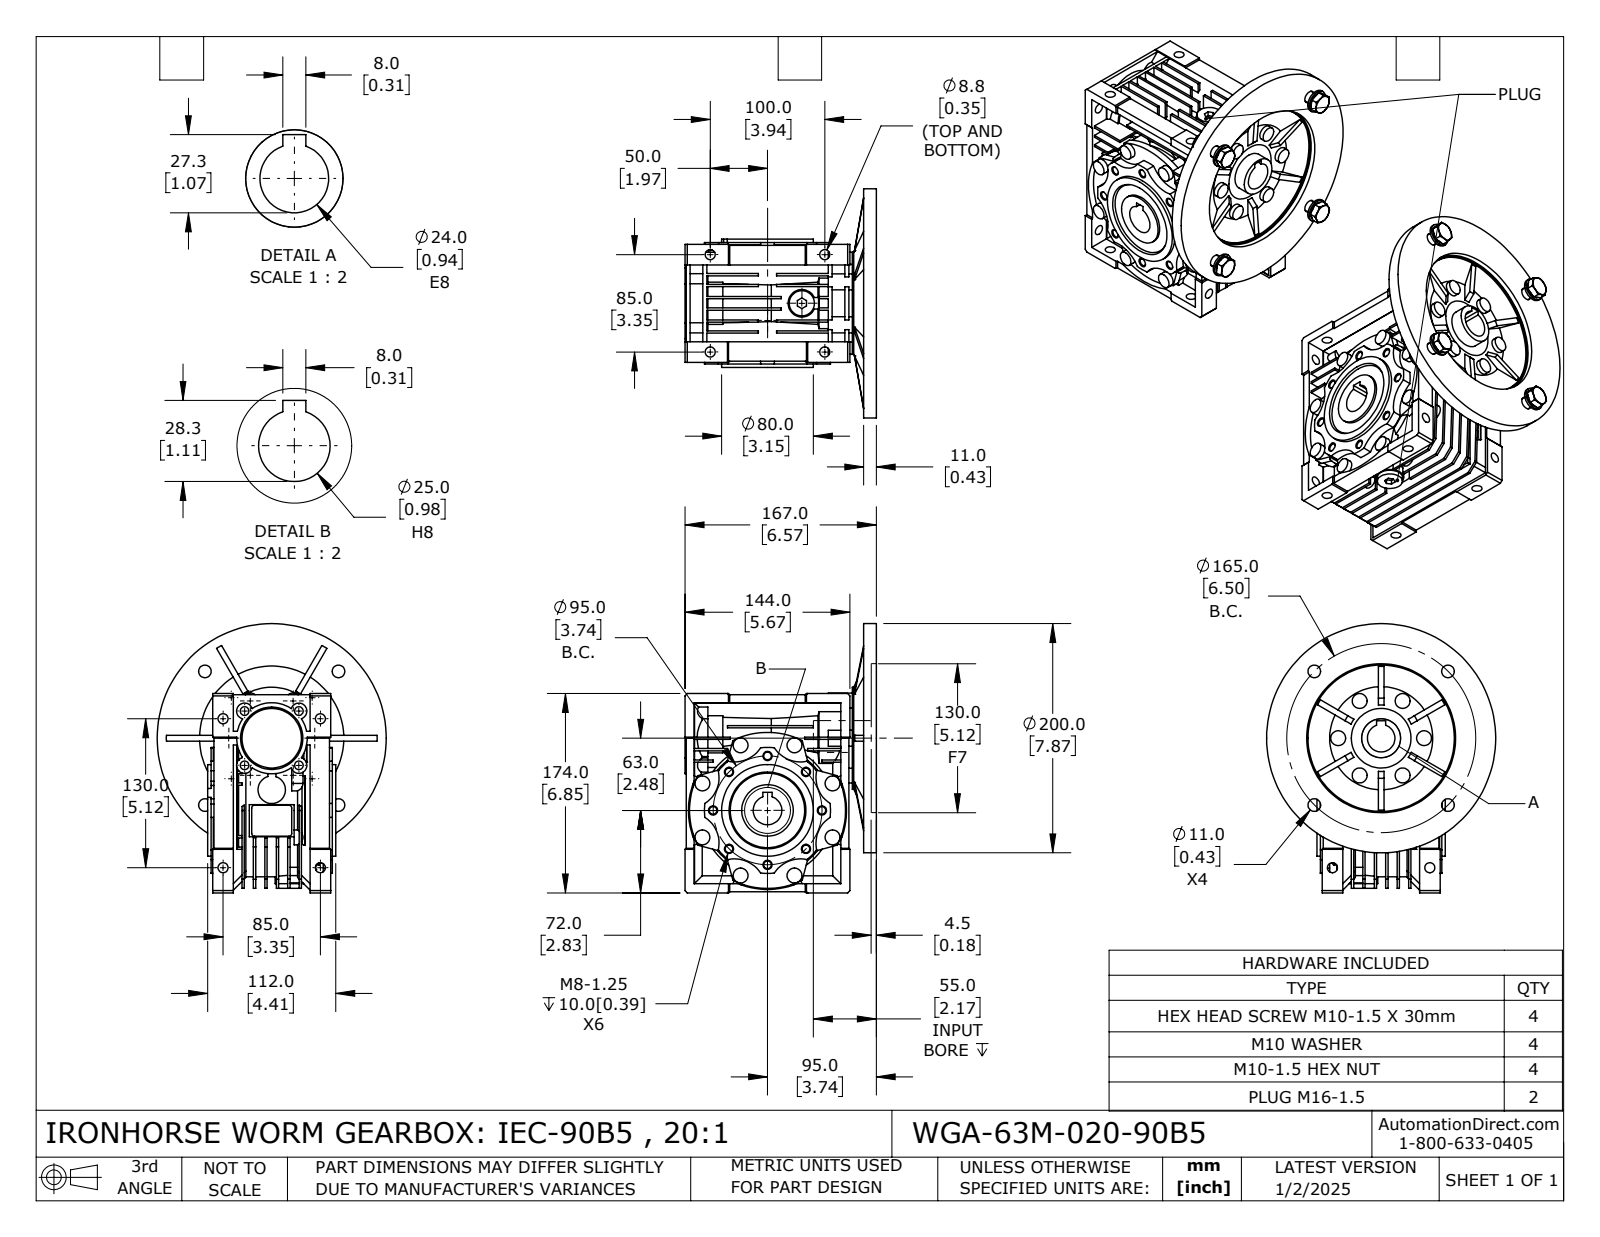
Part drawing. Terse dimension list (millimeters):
name: WGA-63M-020-90B5
written by: SolidWorks 2024 (CONFIG_CONTROL_DESIGN)
unit: mm
bodies: 20 solids, 1529 faces (897 planar, 394 cylindrical, 238 other)
size: 235 × 200 × 183.43
volume: 2 020 000 mm³; area: 402 901 mm²
holes: 8× ⌀6.65, 8× ⌀8.78, 4× ⌀7.56, 4× ⌀8.5, 4× ⌀10, 4× ⌀10.5, 4× ⌀11, 2× ⌀14.5, 2× ⌀25, 1× ⌀24, 1× ⌀34, 1× ⌀37
bosses: 14× ⌀13, 4× ⌀20, 4× ⌀16, 3× ⌀24, 2× ⌀22, 2× ⌀15.8, 2× ⌀13.7, 1× ⌀200
rounds: 10× R7, 8× R27, 4× R2.5, 1× R8.35, 1× R29.5, 1× R30.5, 1× R42, 1× R46
face distances: 10, 8, 20, 2, 11, 30, 12, 7, 40, 18
hole spacings: 36.36, 47.5, 67.18, 87.77, 89.05, 33.5, 47.38, 49
